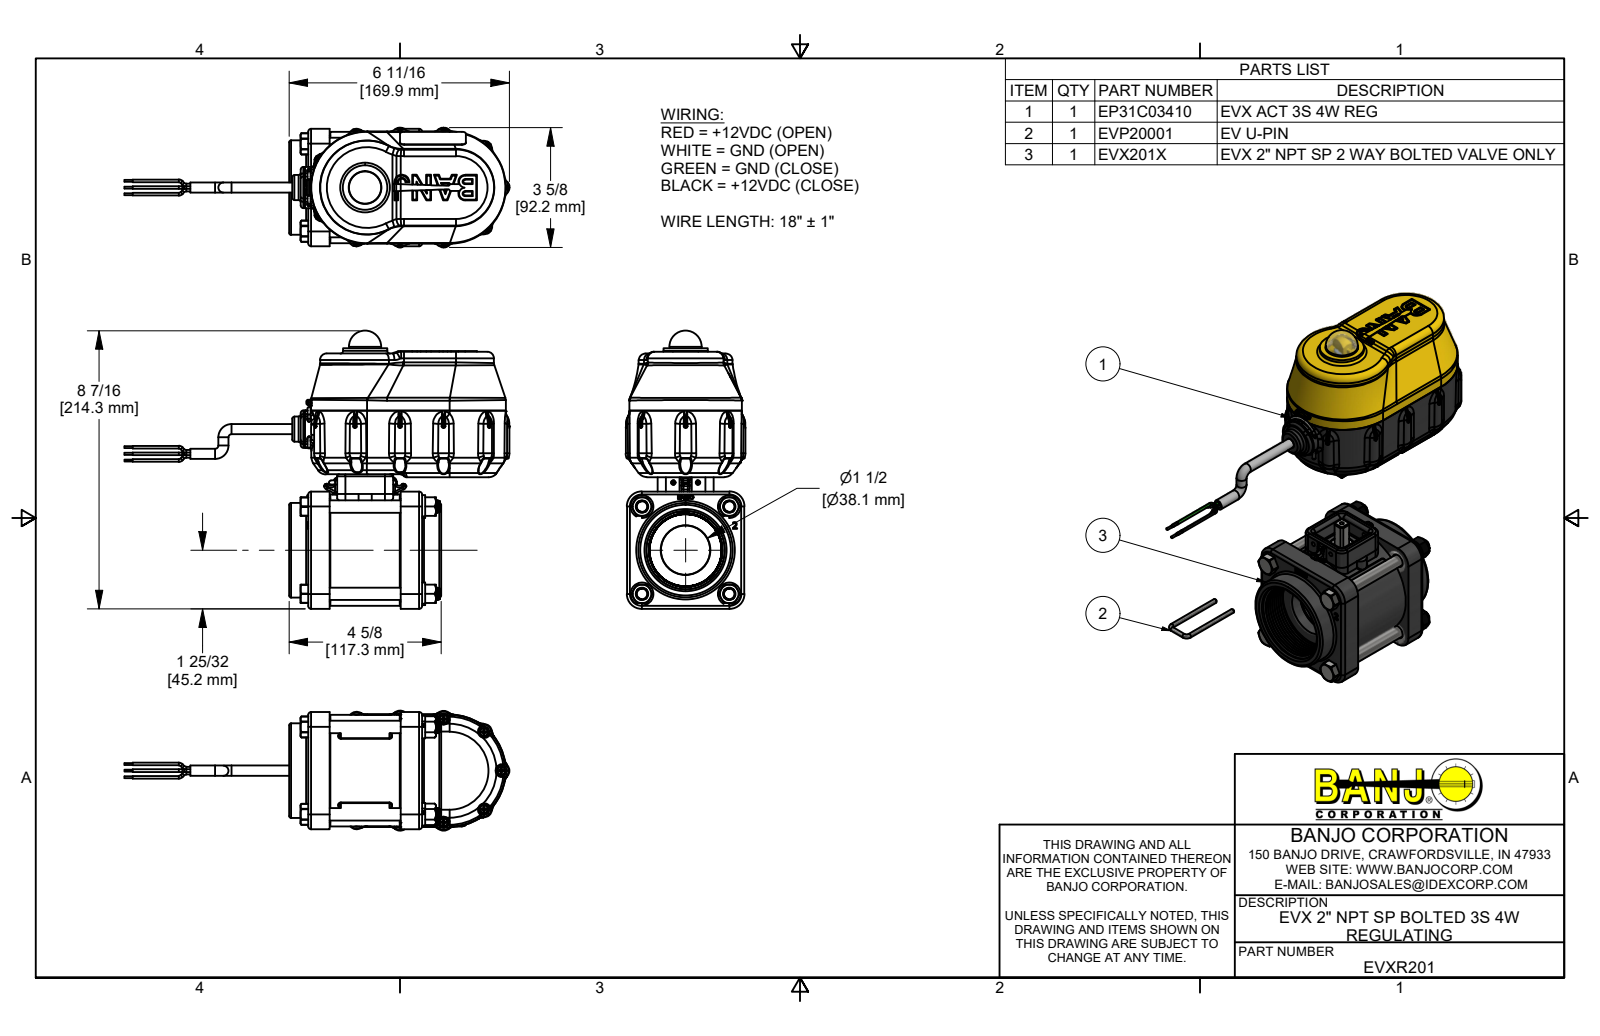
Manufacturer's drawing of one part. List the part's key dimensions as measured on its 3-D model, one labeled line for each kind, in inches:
Part name (STEP PRODUCT): EVXR201; EP31C03410; 91400A119; 95584A200 (+8 more)
STEP written by: Autodesk Inventor 2021 (AUTOMOTIVE_DESIGN)
Units: inches
Bodies: 95 solids, 12761 faces (3656 planar, 3357 cylindrical, 5748 other)
Overall size (bounding box): 11.685 × 8.437 × 3.63
Volume: 59.72 in³ · Surface area: 652.9 in²
Round holes (diameter × count): ⌀0.15 ×13, ⌀0.095 ×11, ⌀0.107 ×4, ⌀0.126 ×4, ⌀0.136 ×4, ⌀0.17 ×4, ⌀0.307 ×4, ⌀0.385 ×4, ⌀0.42 ×4, ⌀0.135 ×3, ⌀0.089 ×2, ⌀0.105 ×2
Round bosses / shafts (diameter × count): ⌀0.324 ×60, ⌀0.08 ×20, ⌀0.25 ×17, ⌀0.14 ×11, ⌀0.108 ×11, ⌀0.085 ×11, ⌀0.058 ×8, ⌀0.375 ×5
Partial cylindrical surfaces — rounded edges, fillets, slot ends (radius × count): R0.04 ×147, R0.02 ×112, R0.01 ×58, R0.005 ×47, R0.015 ×36, R0.03 ×35, R0.06 ×32, R0.08 ×28
Main face-to-face distances: 0.1, 2.565, 0.65, 2.808, 1.685, 0.525, 0.78, 2.465, 2.63, 3.56
Hole centre spacings: 1.872, 2.648, 1.662, 2.088, 2.73, 3.45, 3.509, 3.781
